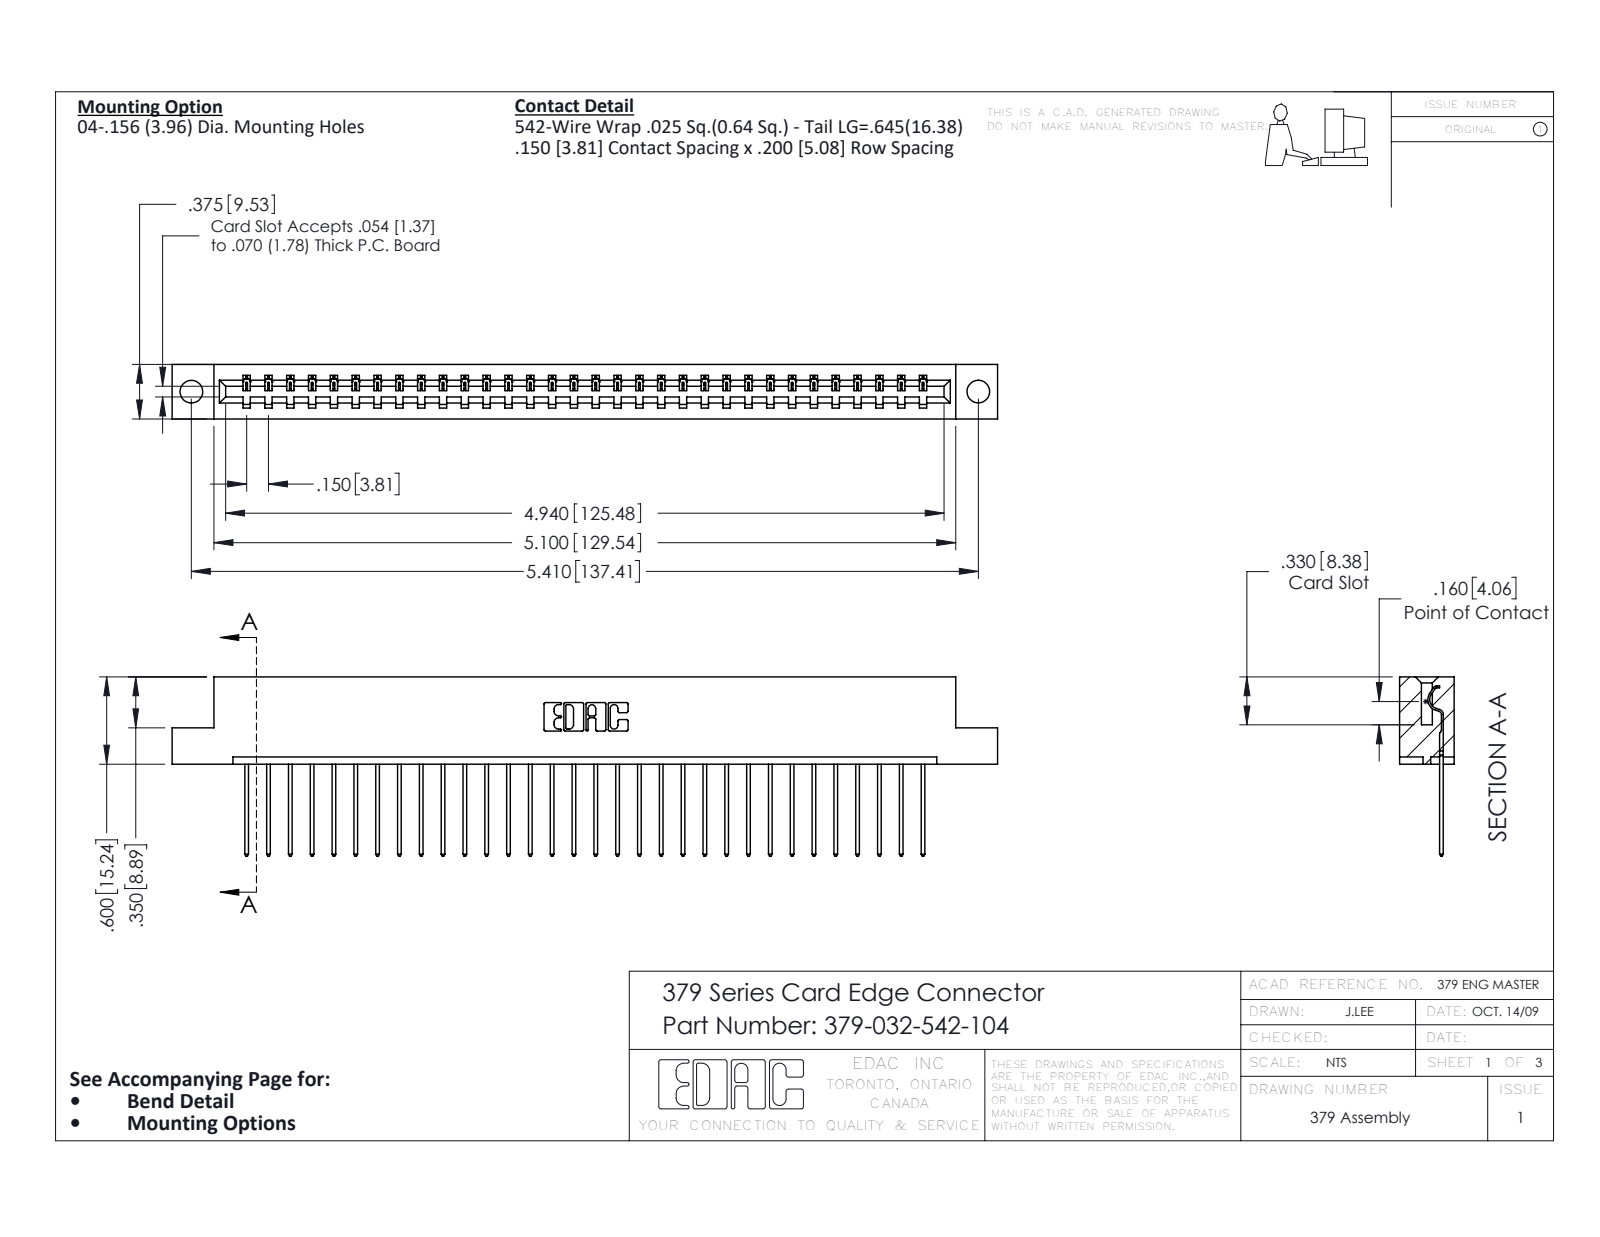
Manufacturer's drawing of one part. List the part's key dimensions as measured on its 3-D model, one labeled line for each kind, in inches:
Part name (STEP PRODUCT): 379-032-542-104; 345-292-001_345-293-142; 379 Part_Flush - .156 Dia - TH
STEP written by: SolidWorks 2016 (CONFIG_CONTROL_DESIGN)
Units: inches
Bodies: 33 solids, 1970 faces (1414 planar, 556 cylindrical, 0 other)
Overall size (bounding box): 5.675 × 1.232 × 0.375
Volume: 0.916 in³ · Surface area: 24.13 in²
Round holes (diameter × count): ⌀0.156 ×2
Partial cylindrical surfaces — rounded edges, fillets, slot ends (radius × count): R0.006 ×64, R0.01 ×64, R0.01 ×22, R0.007 ×6, R0.031 ×6, R0.026 ×3, R0.014 ×1, R0.022 ×1
Main face-to-face distances: 0.3, 0.075, 0.375, 0.225, 0.275, 0.1, 0.025, 0.2, 0.6, 0.55
Hole centre spacings: 5.41
